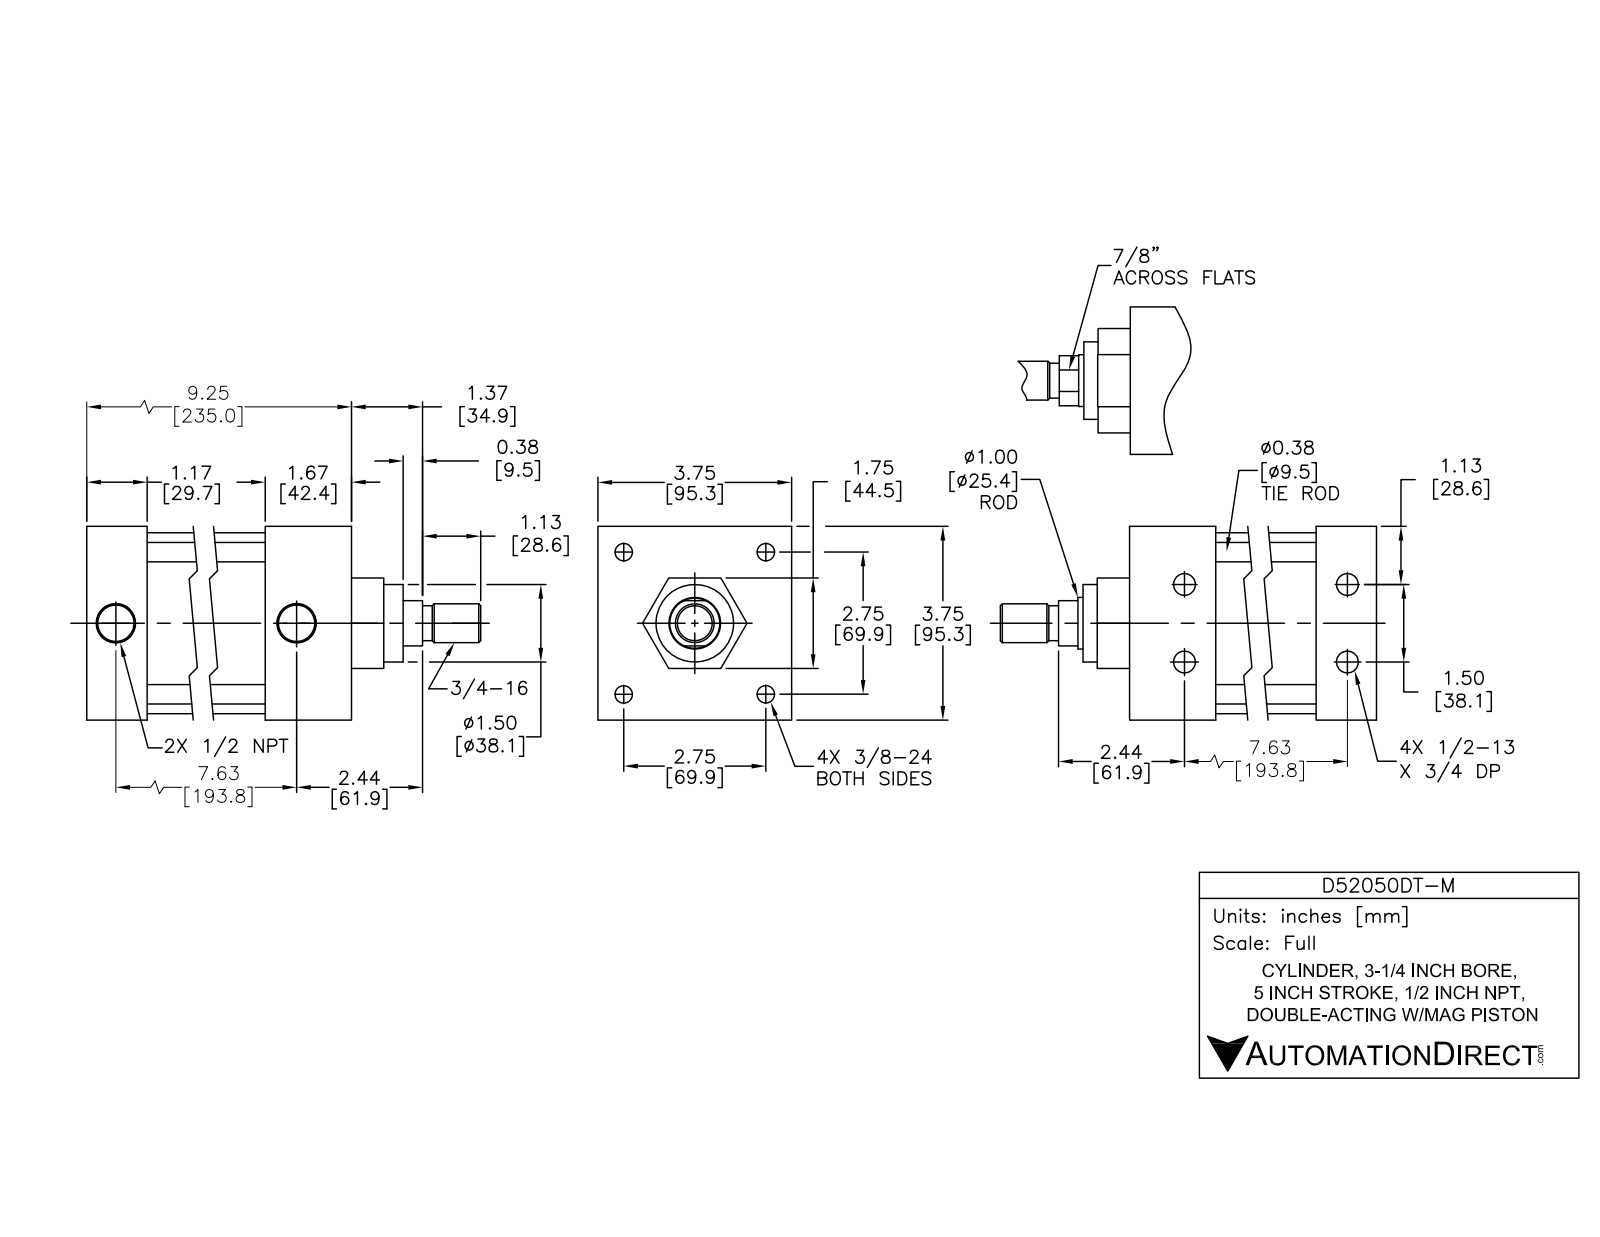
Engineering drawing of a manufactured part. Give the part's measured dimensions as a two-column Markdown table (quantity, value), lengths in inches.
| quantity | value |
| --- | --- |
| part name | D52050DT-M BODY; D52050DT-M PISTON; D52050DT-M |
| STEP written by | SolidWorks 2015 (AUTOMOTIVE_DESIGN) |
| units | inches |
| bodies | 12 solids, 303 faces (99 planar, 114 cylindrical, 90 other) |
| overall size | 11.745 × 3.75 × 3.75 |
| volume | 66.17 in³ |
| surface area | 380.1 in² |
| round holes (diameter × count) | 0.33 × 4, 0.406 × 4, 0.417 × 4, 0.625 × 4, 0.5 × 2, 0.766 × 2, 1 × 1, 1.003 × 1, 3.25 × 1 |
| round bosses / shafts (diameter × count) | 0.609 × 4, 0.375 × 4, 0.34 × 4, 3.5 × 1, 3.247 × 1, 1.75 × 1, 0.997 × 1, 0.97 × 1 |
| partial cylindrical surfaces (radius × count) | 0.375 × 4 |
| main face-to-face distances | 3.75, 0.08, 6.326, 9.246, 1.75, 7.997, 1.249, 6.751, 1.246, 2.495 |
| hole center spacings | 0.75, 0.76, 1.5, 1.95, 1.95, 2.758, 2.758, 3.9 |
